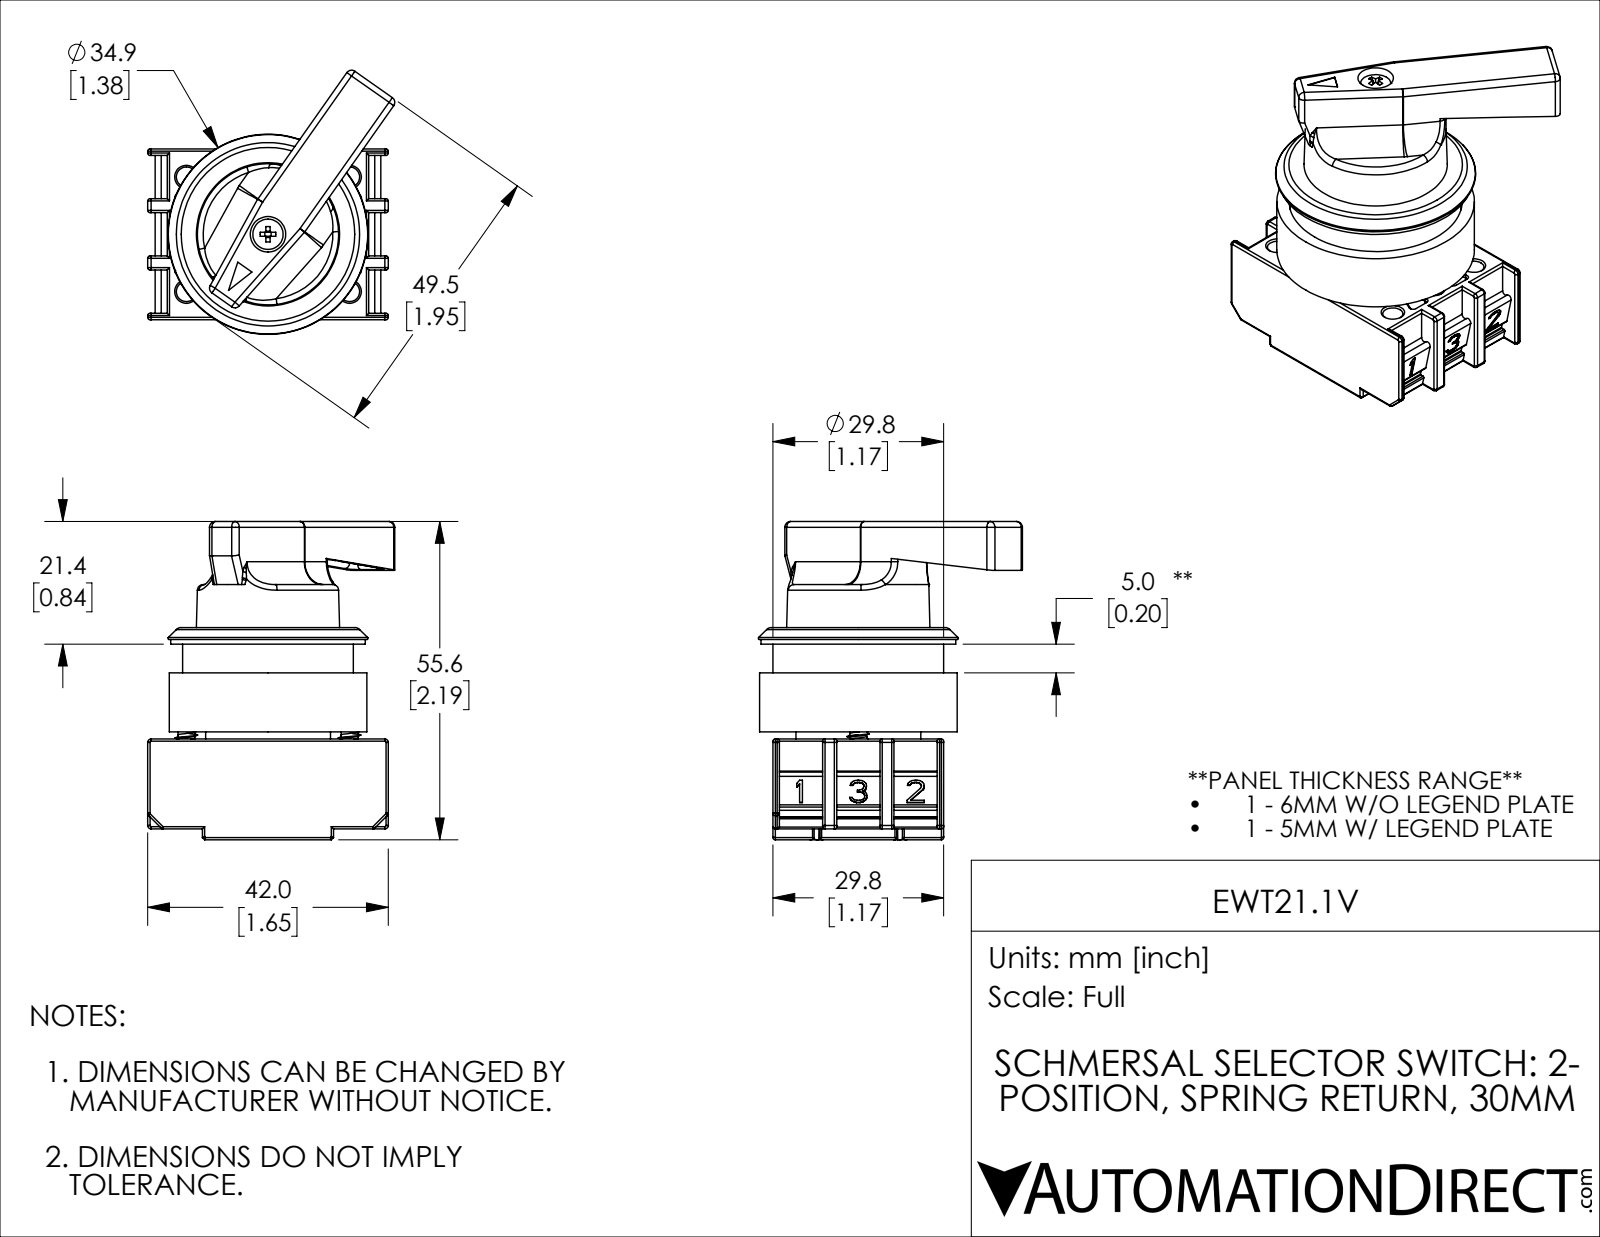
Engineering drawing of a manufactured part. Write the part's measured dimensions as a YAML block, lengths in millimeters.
part_name: "EWT21.1V"
step_written_by: "SolidWorks 2019 (CONFIG_CONTROL_DESIGN)"
units: millimeters
bodies: {solids: 5, faces: 1671, planar: 617, cylindrical: 563, other: 491}
overall_size: [55.55, 46.1, 43.14]
volume: 30088
surface_area: 26026
round_holes:
  - {diameter: 3.5, count: 6}
  - {diameter: 5.15, count: 6}
  - {diameter: 6.2, count: 1}
  - {diameter: 9.15, count: 1}
  - {diameter: 9.9, count: 1}
  - {diameter: 11, count: 1}
  - {diameter: 14, count: 1}
  - {diameter: 19, count: 1}
  - {diameter: 22, count: 1}
  - {diameter: 24.2, count: 1}
  - {diameter: 26, count: 1}
  - {diameter: 30.2, count: 1}
round_bosses_or_shafts:
  - {diameter: 4.8, count: 2}
  - {diameter: 2.93, count: 2}
  - {diameter: 34.5, count: 1}
  - {diameter: 34, count: 1}
  - {diameter: 29.8, count: 1}
  - {diameter: 25.5, count: 1}
  - {diameter: 21.8, count: 1}
  - {diameter: 18.5, count: 1}
partial_cylinders:
  - {radius: 0.4, count: 110}
  - {radius: 0.3, count: 48}
  - {radius: 1, count: 40}
  - {radius: 0.2, count: 26}
  - {radius: 0.5, count: 16}
  - {radius: 0.6, count: 8}
  - {radius: 0.8, count: 6}
  - {radius: 4, count: 4}
face_to_face_distances: [16.1, 17.35, 18.85, 10, 29.8, 37.05, 22.5, 18.2, 1.9, 4.2]
hole_center_spacings: [10, 17.41, 30.2, 28.5, 14.25, 20, 34.82]
